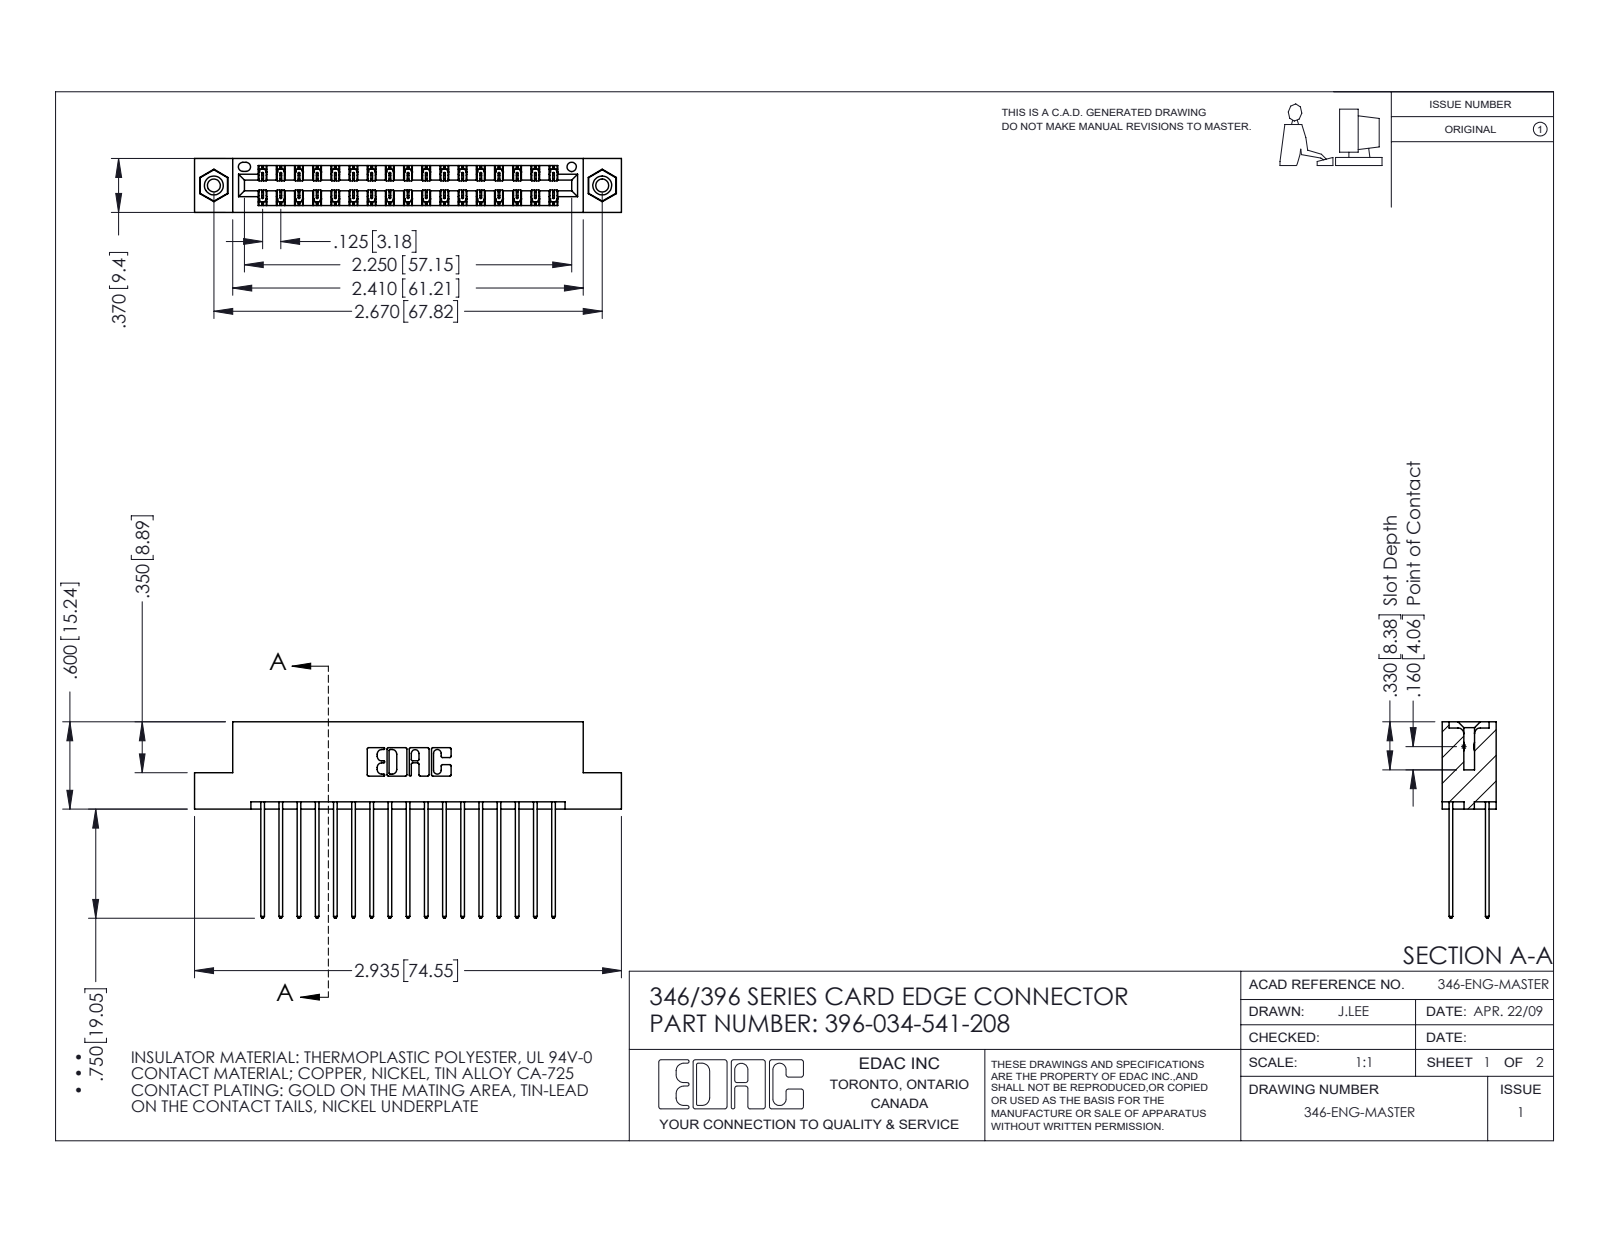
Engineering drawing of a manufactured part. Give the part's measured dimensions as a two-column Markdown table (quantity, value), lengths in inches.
| quantity | value |
| --- | --- |
| part name | 346 Part_Flush Mounting Lugs - 0.156 Dia-TI; 345-250-001_345-250-003-102; 345-292-001_345-293-141; 396-034-541-208 |
| STEP written by | SolidWorks 2016 (CONFIG_CONTROL_DESIGN) |
| units | inches |
| bodies | 37 solids, 1950 faces (1298 planar, 636 cylindrical, 16 other) |
| overall size | 2.935 × 1.35 × 0.37 |
| volume | 0.443 in³ |
| surface area | 16.35 in² |
| round holes (diameter × count) | 0.089 × 2, 0.125 × 2, 0.156 × 2, 0.064 × 1 |
| round bosses / shafts (diameter × count) | 0.155 × 2 |
| partial cylindrical surfaces (radius × count) | 0.006 × 51, 0.01 × 34, 0.01 × 22, 0.007 × 6, 0.031 × 6, 0.026 × 3, 0.014 × 2, 0.022 × 2 |
| main face-to-face distances | 0.048, 0.322, 0.25, 0.072, 0.298, 0.025, 0.37, 0.275, 0.148, 0.222 |
| hole center spacings | 0.246, 2.463, 2.67 |
